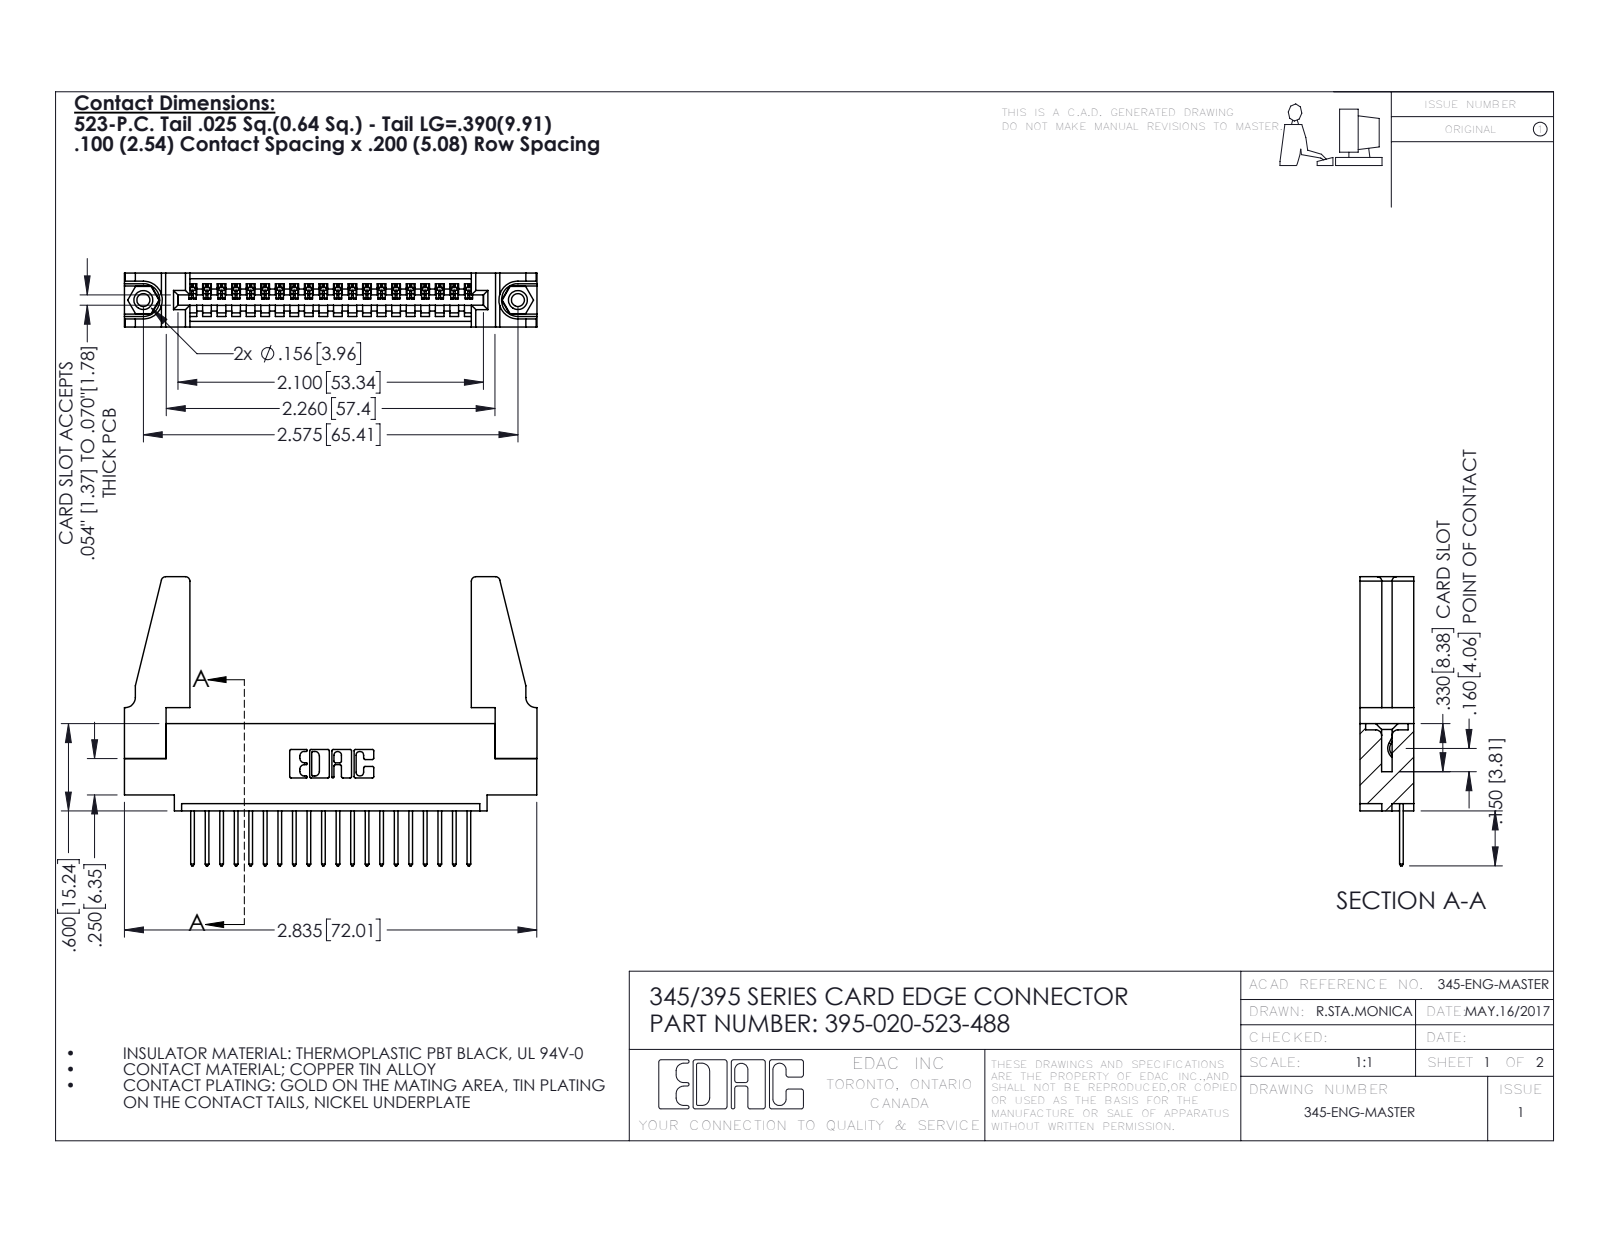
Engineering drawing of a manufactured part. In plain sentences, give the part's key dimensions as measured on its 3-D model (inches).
The part is named "345-250-001_345-250-001-102; 345-292-001_345-293-123; 345-220-078_345-220-088; 345 Part_0.110 Offset - 0.156 Dia-TH (+1 more)". Its 3-D file was written by "SolidWorks 2016 (CONFIG_CONTROL_DESIGN)". It is 25 solids with 1414 faces: 956 planar, 442 cylindrical and 16 other. Overall it measures 2.836 by 1.987 by 0.37 inches. Its volume is 0.6 cubic inches and its surface area 18.1 square inches. Round holes: 2 of diameter 0.089, 2 of diameter 0.125, 2 of diameter 0.156, 1 of diameter 0.064. Round bosses or shafts: 2 of diameter 0.155. Partial cylindrical surfaces (rounded edges, fillets, slot ends): 40 of radius 0.006, 40 of radius 0.01, 22 of radius 0.01, 8 of radius 0.03, 6 of radius 0.007, 6 of radius 0.031, 3 of radius 0.026, 2 of radius 0.031. The main face-to-face distances are 0.37, 0.072, 0.298, 0.2, 0.098, 0.272, 0.025, 0.225, 0.148, 0.15. The hole center spacings are 0.27, 2.341, 2.575.
